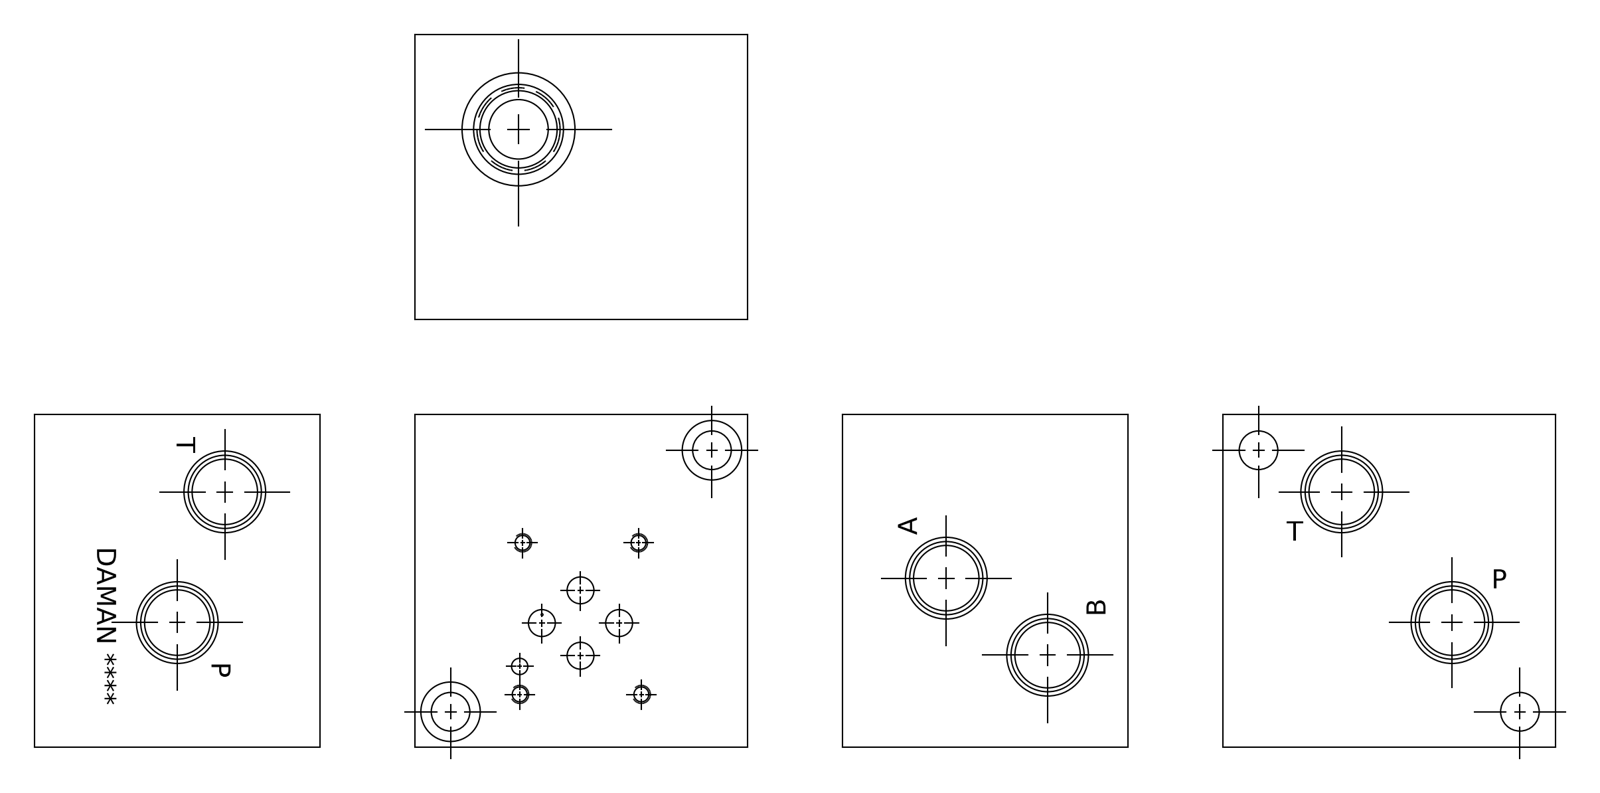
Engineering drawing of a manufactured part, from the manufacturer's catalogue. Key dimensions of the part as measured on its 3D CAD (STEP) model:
Part name (STEP PRODUCT): Part_AD03SPRVC8P.C11865R2_3D
STEP written by: Autodesk Inventor 2019 (AUTOMOTIVE_DESIGN)
Units: millimetres
Bodies: 1 solid, 525 faces (313 planar, 38 cylindrical, 174 other)
Overall size (bounding box): 88.9 × 88.9 × 76.2
Volume: 520 999 mm³ · Surface area: 61 685 mm²
Round holes (diameter × count): ⌀17.48 ×6, ⌀21.59 ×6, ⌀3.78 ×4, ⌀4.83 ×4, ⌀7.14 ×4, ⌀7.95 ×2, ⌀10.31 ×2, ⌀15.88 ×2, ⌀4.37 ×1, ⌀14.29 ×1, ⌀14.3 ×1, ⌀15.9 ×1
Main face-to-face distances: 88.9, 76.2, 15.37, 73.53, 80.72, 8.18, 58.16, 60.83, 61.93, 46.56
Hole centre spacings: 22.05, 33.55, 33.91, 40.5, 51.45, 67.73, 6.35, 7.5
